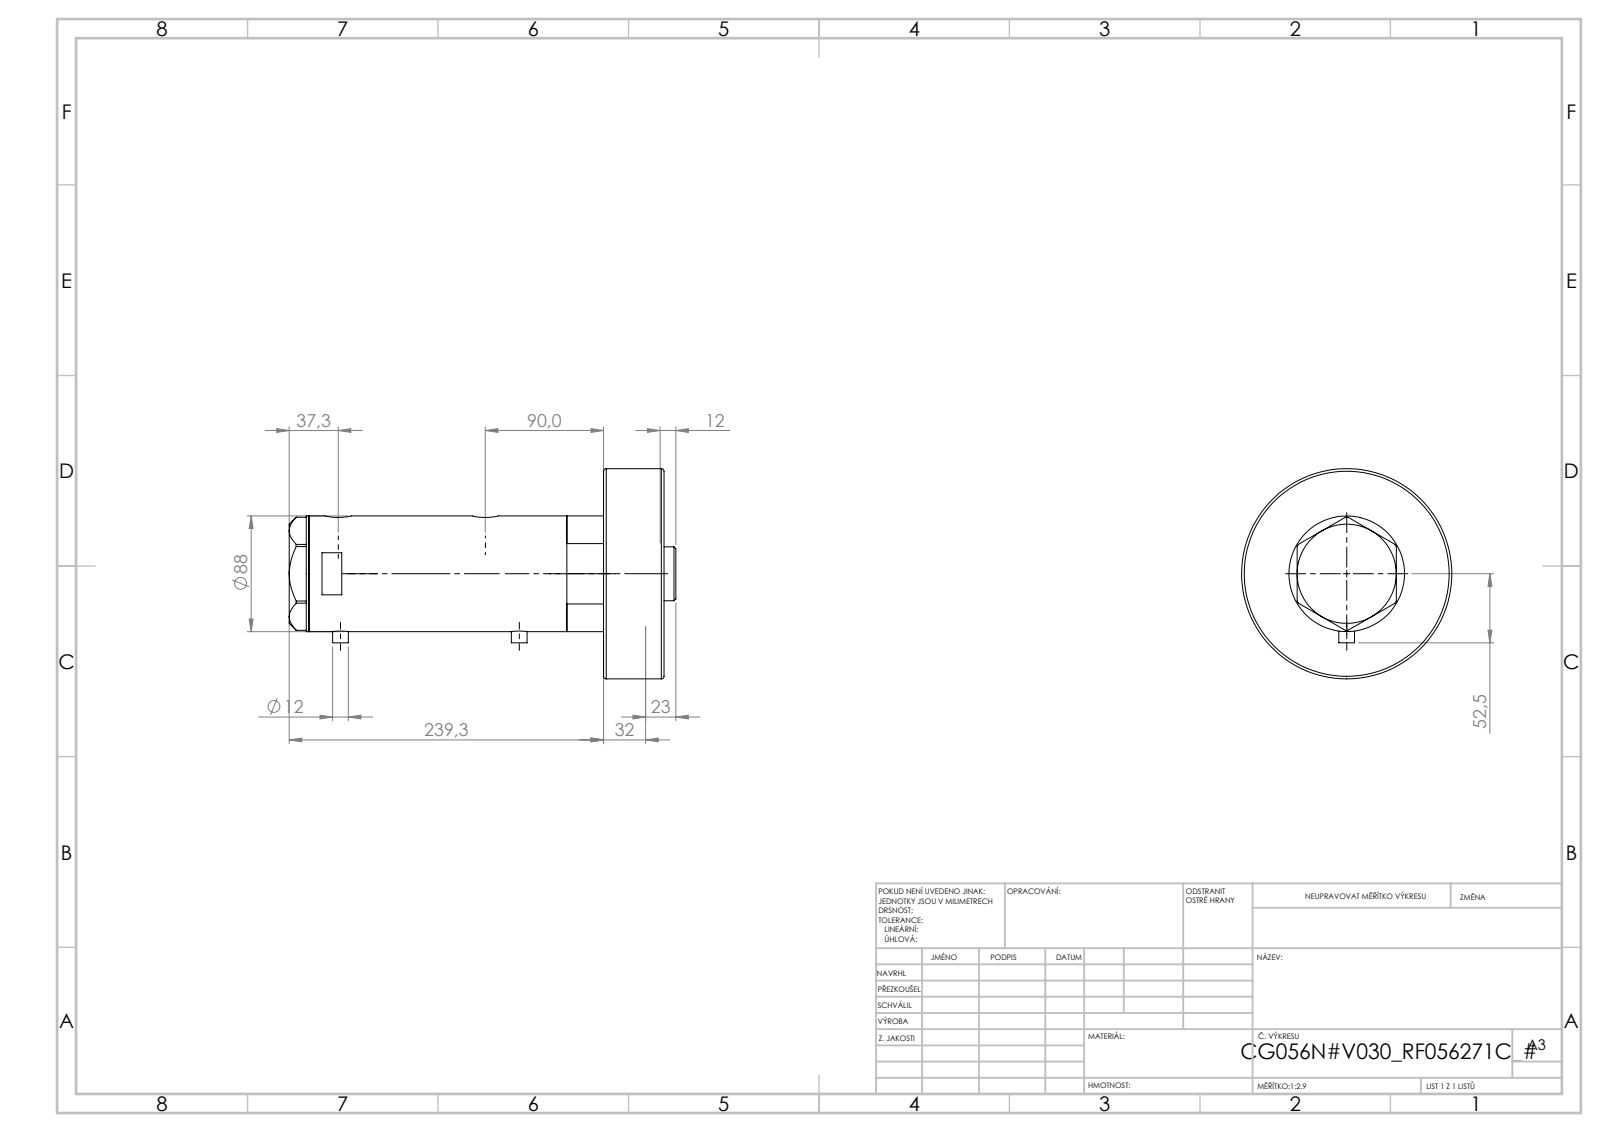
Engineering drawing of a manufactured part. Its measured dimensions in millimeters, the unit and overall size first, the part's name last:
Units: millimetres
Overall size (bounding box): 294.3 × 160 × 160
Round holes (diameter × count): ⌀12.5 ×2, ⌀13.16 ×2, ⌀20 ×2, ⌀14.5 ×1, ⌀42 ×1, ⌀43.5 ×1, ⌀56 ×1, ⌀60 ×1, ⌀75 ×1, ⌀80 ×1
Round bosses / shafts (diameter × count): ⌀12 ×2, ⌀160 ×1, ⌀88 ×1, ⌀73 ×1, ⌀41 ×1
Main face-to-face distances: 46, 224.3, 270.3, 134.4, 89.9, 135.9, 244.3, 26, 108.4, 198.3
Hole centre spacings: 1.7, 25.8, 110.3, 112, 136.1, 137.8
Volume: 2 276 000 mm³ · Surface area: 286 784 mm²
Bodies: 5 solids, 131 faces (54 planar, 53 cylindrical, 24 other)
Part name (STEP PRODUCT): V270CG_FRONT; V270CG_VC; V270CG_MIDDLE; V270CG_BACK (+1 more)
STEP written by: SolidWorks 2019 (CONFIG_CONTROL_DESIGN)
